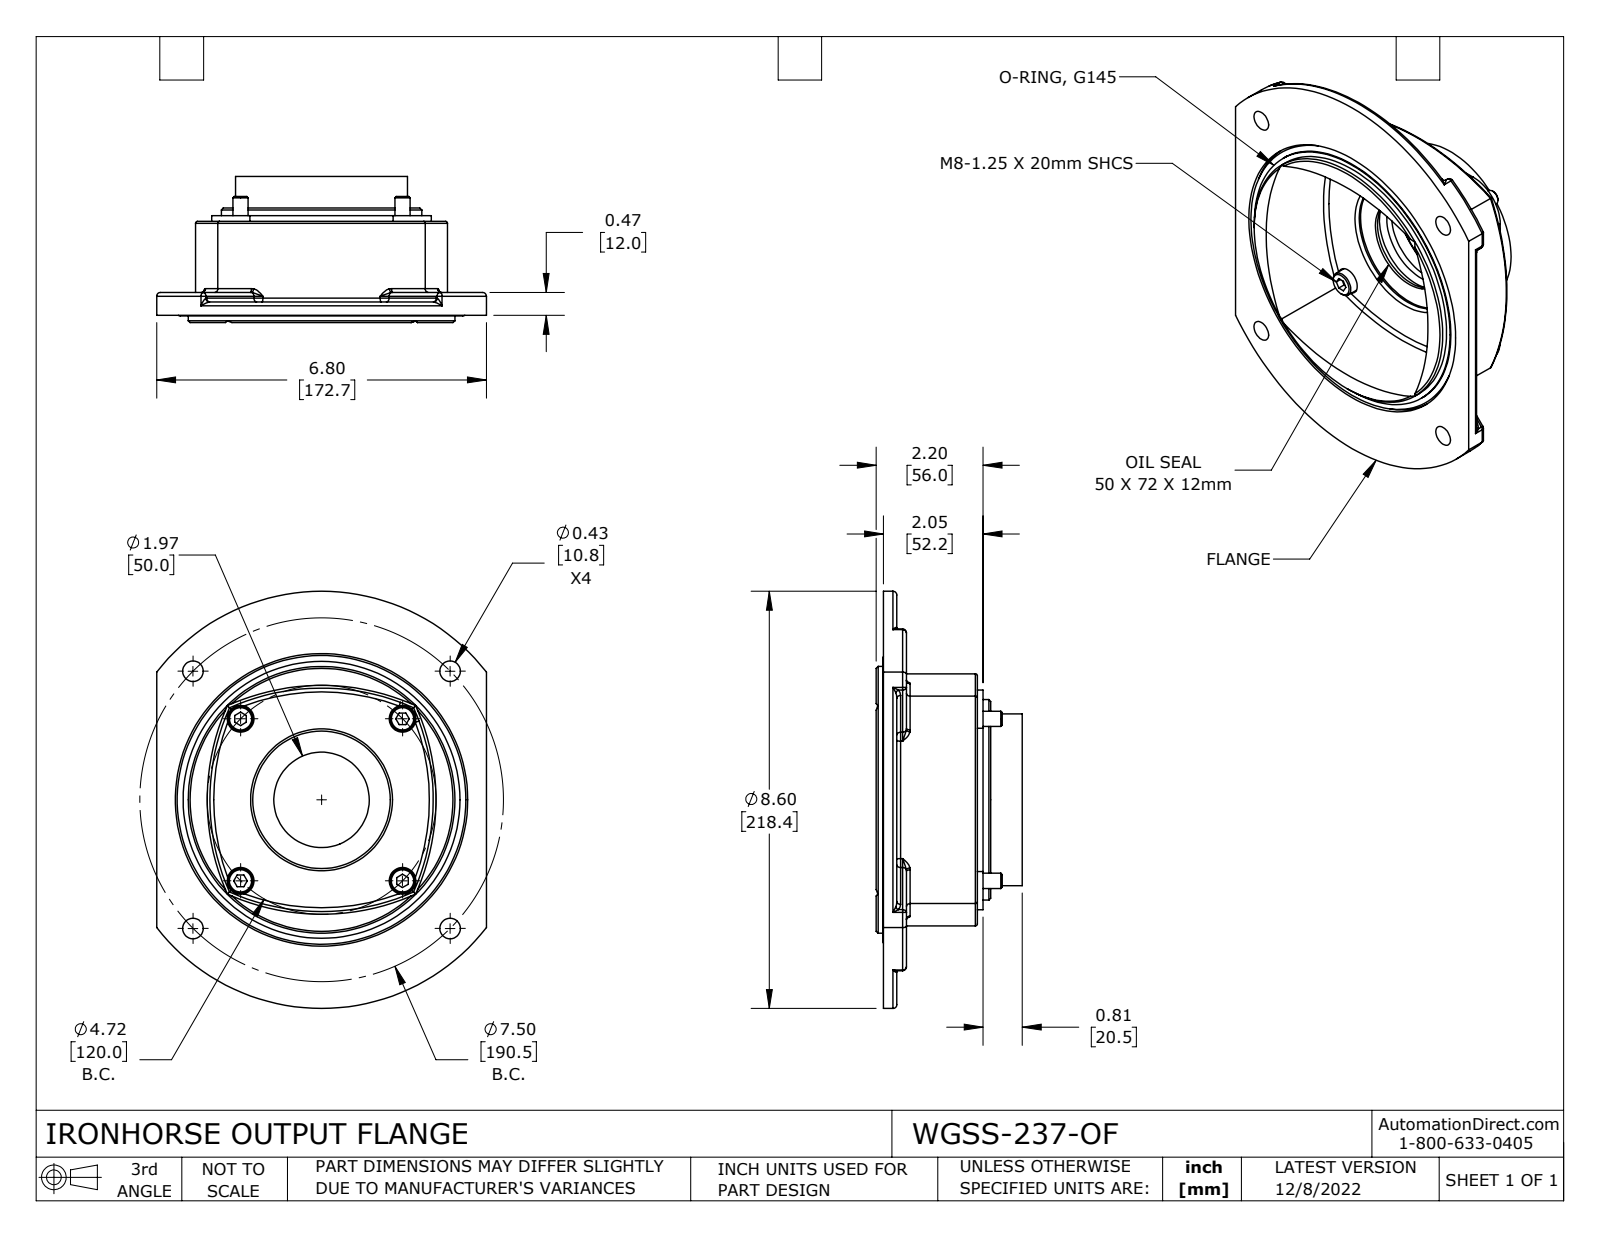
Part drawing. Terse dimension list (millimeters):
name: WGSS-237-OF
written by: SolidWorks 2021 (CONFIG_CONTROL_DESIGN)
unit: mm
bodies: 7 solids, 336 faces (85 planar, 119 cylindrical, 132 other)
size: 218.44 × 172.72 × 76.5
volume: 483 985 mm³; area: 140 623 mm²
holes: 4× ⌀9, 4× ⌀10.8, 4× ⌀14, 1× ⌀50, 1× ⌀64, 1× ⌀67, 1× ⌀72, 1× ⌀73, 1× ⌀80, 1× ⌀153.2
bosses: 4× ⌀13, 4× ⌀8, 1× ⌀145, 1× ⌀139.7, 1× ⌀105, 1× ⌀90, 1× ⌀58
rounds: 24× R2, 8× R5, 4× R20, 4× R132, 1× R109.22
face distances: 7, 12, 39.19, 42.19, 5, 32.19, 3, 10, 27.19, 45.19
hole spacings: 112.57, 35.24, 60.01, 84.86, 95.25, 134.7, 155.25, 120.01
